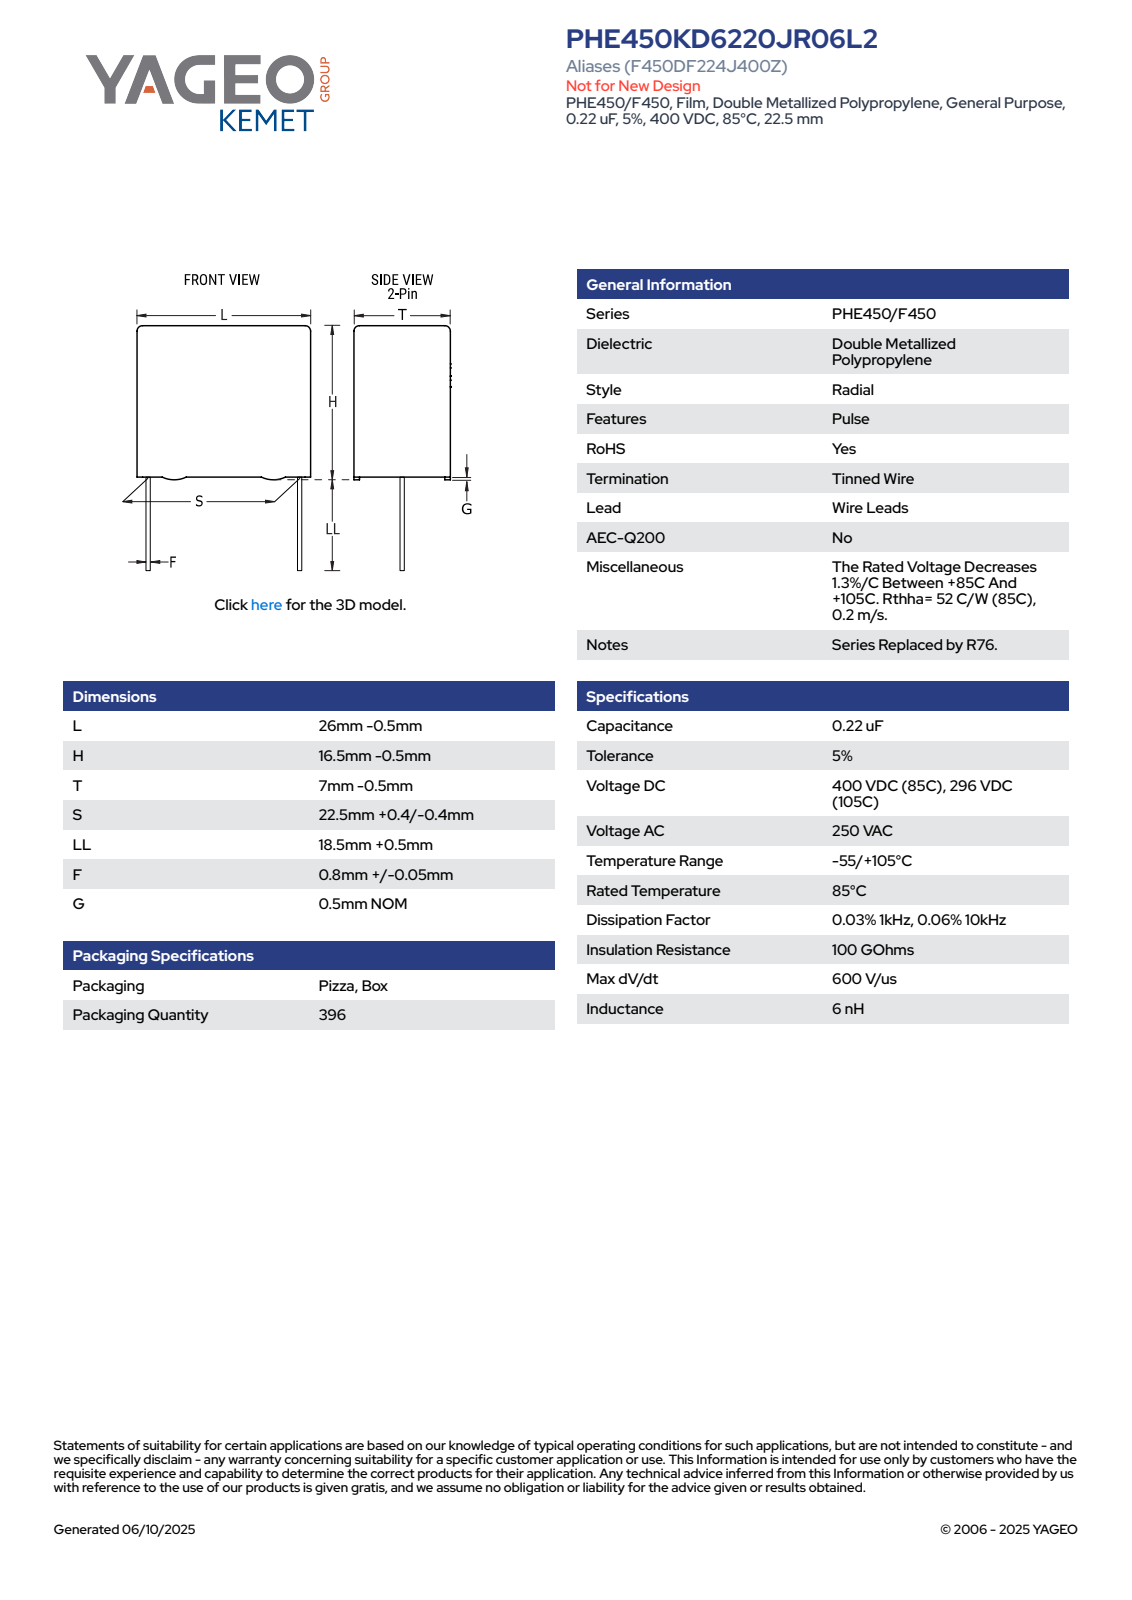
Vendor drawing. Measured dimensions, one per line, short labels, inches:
name: CFR_RBG_26X16.5X7_L26H16.5T7S22.5LL19F0.85G0.5
written by: SolidWorks 2014 (AUTOMOTIVE_DESIGN)
unit: in
bodies: 4 solids, 89 faces (81 planar, 8 cylindrical, 0 other)
size: 1.398 × 1.024 × 0.276
volume: 0.179 in³; area: 2.48 in²
bosses: 2× ⌀0.033
rounds: 4× R0.02
face distances: 0.276, 0.63, 1.024, 0.016, 0.26, 0.02, 0.65, 0.244, 0.748, 0.768
